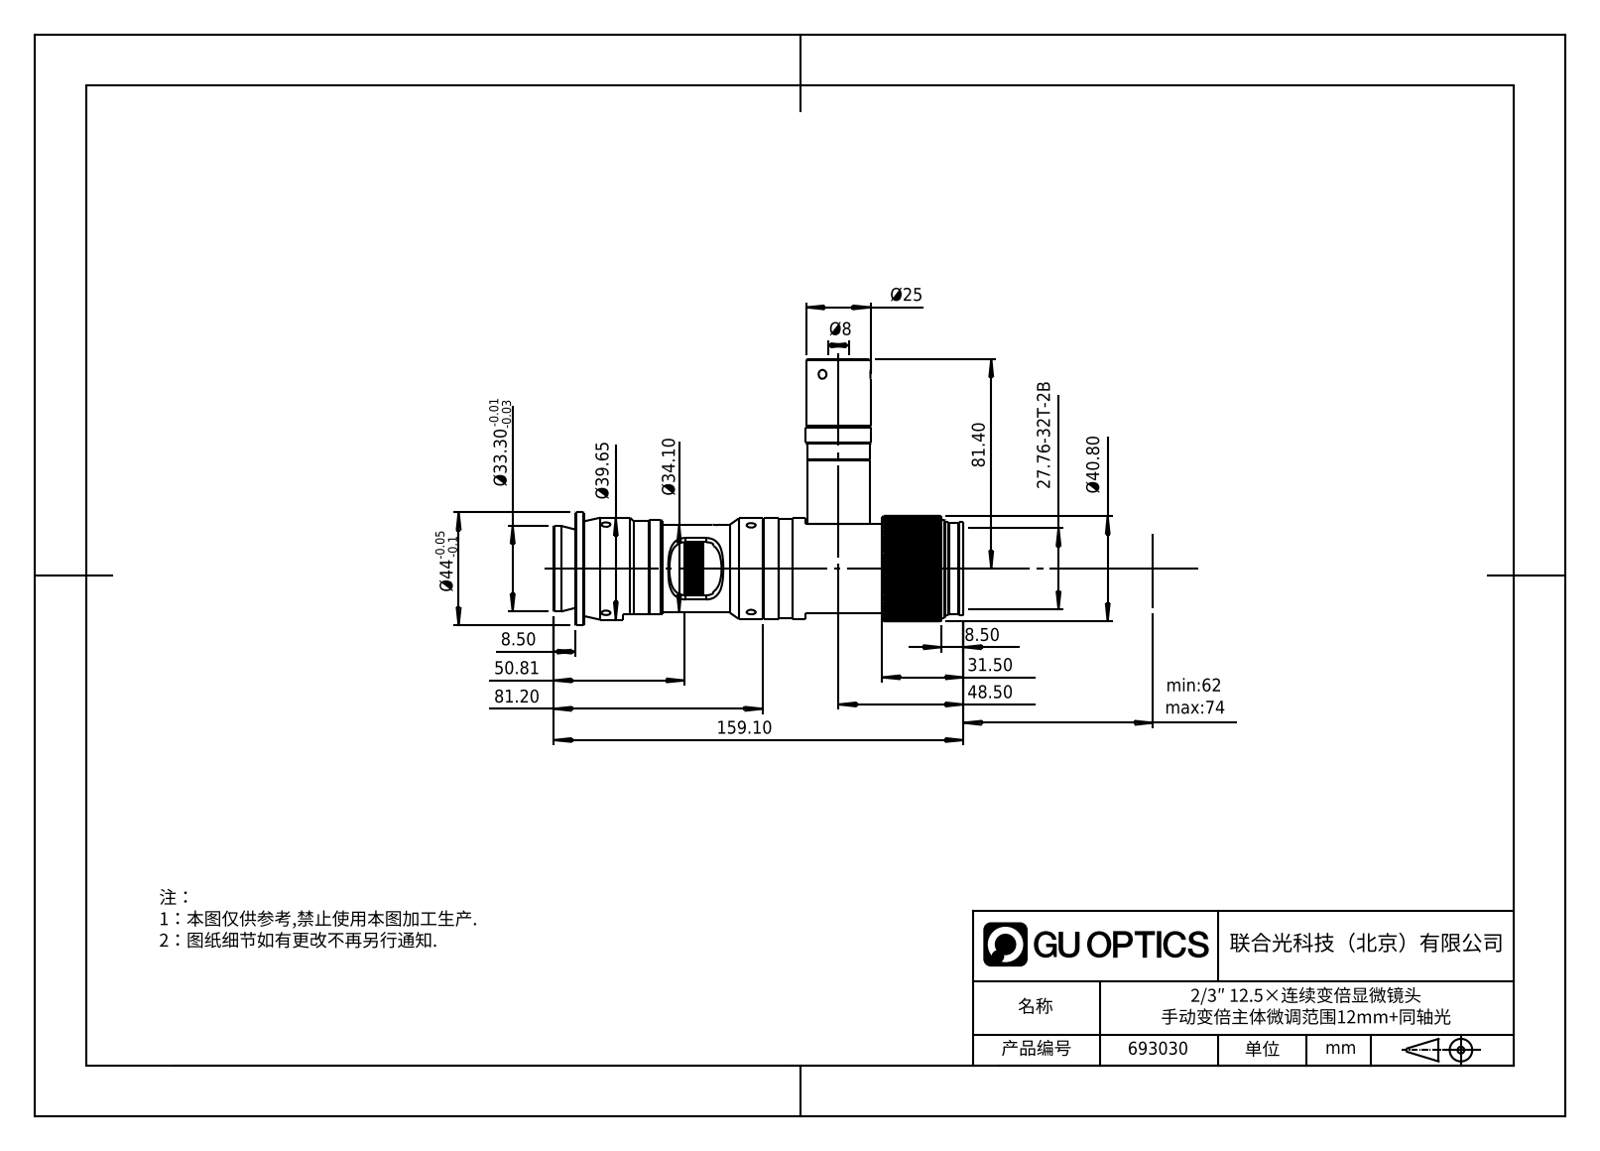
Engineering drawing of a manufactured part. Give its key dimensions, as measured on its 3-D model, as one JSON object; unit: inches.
{"part_name": "693030", "step_written_by": "SolidWorks 2020 (CONFIG_CONTROL_DESIGN)", "units": "inches", "bodies": {"solids": 0, "faces": 1024, "planar": 580, "cylindrical": 336, "other": 108}, "overall_size": [6.264, 4.071, 1.732], "round_holes": [[0.138, 10], [0.063, 4], [0.037, 3], [0.059, 3], [0.118, 3], [0.043, 2], [0.069, 2], [0.087, 1], [0.12, 1], [0.157, 1], [0.315, 1], [0.472, 1]], "round_bosses_or_shafts": [[0.087, 3], [0.047, 3], [1.732, 1], [1.561, 1], [1.535, 1], [1.512, 1], [1.5, 1], [1.496, 1]], "partial_cylinders_radius": [[0.049, 6], [0.276, 4], [0.616, 1], [0.803, 1]], "face_to_face_distances": [0.039, 0.13, 4.689, 2.732, 4.559, 2.862, 1.827, 1.113, 4.728, 4.598], "hole_center_spacings": [0.713, 1.234, 2.219, 0.389, 0.581, 1.343, 3.203, 0.217]}
